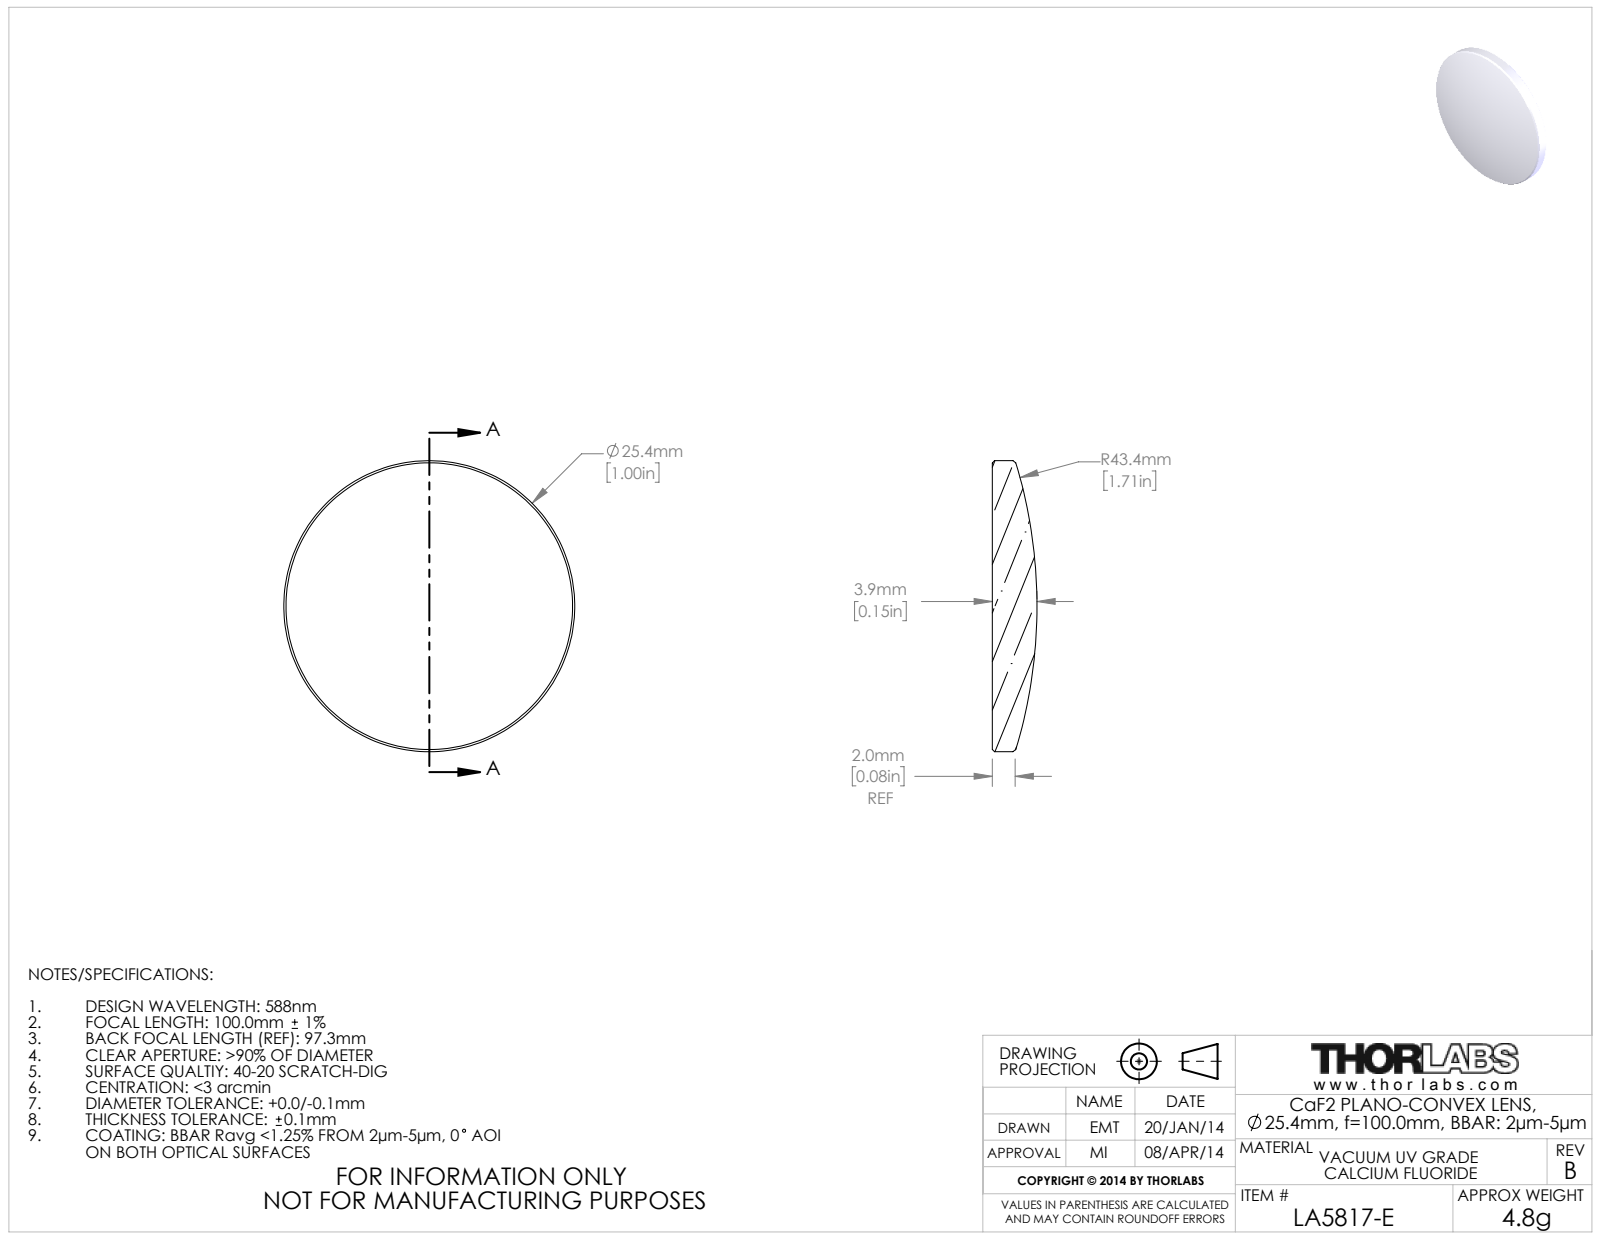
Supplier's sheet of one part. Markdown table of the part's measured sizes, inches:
| quantity | value |
| --- | --- |
| part name | 20134-E0W |
| STEP written by | SolidWorks 2018 (CONFIG_CONTROL_DESIGN) |
| units | inches |
| bodies | 1 solid, 9 faces (1 planar, 2 cylindrical, 6 other) |
| overall size | 1 × 1 × 0.154 |
| volume | 0.091 in³ |
| surface area | 1.812 in² |
| round bosses / shafts (diameter × count) | 1 × 1 |
